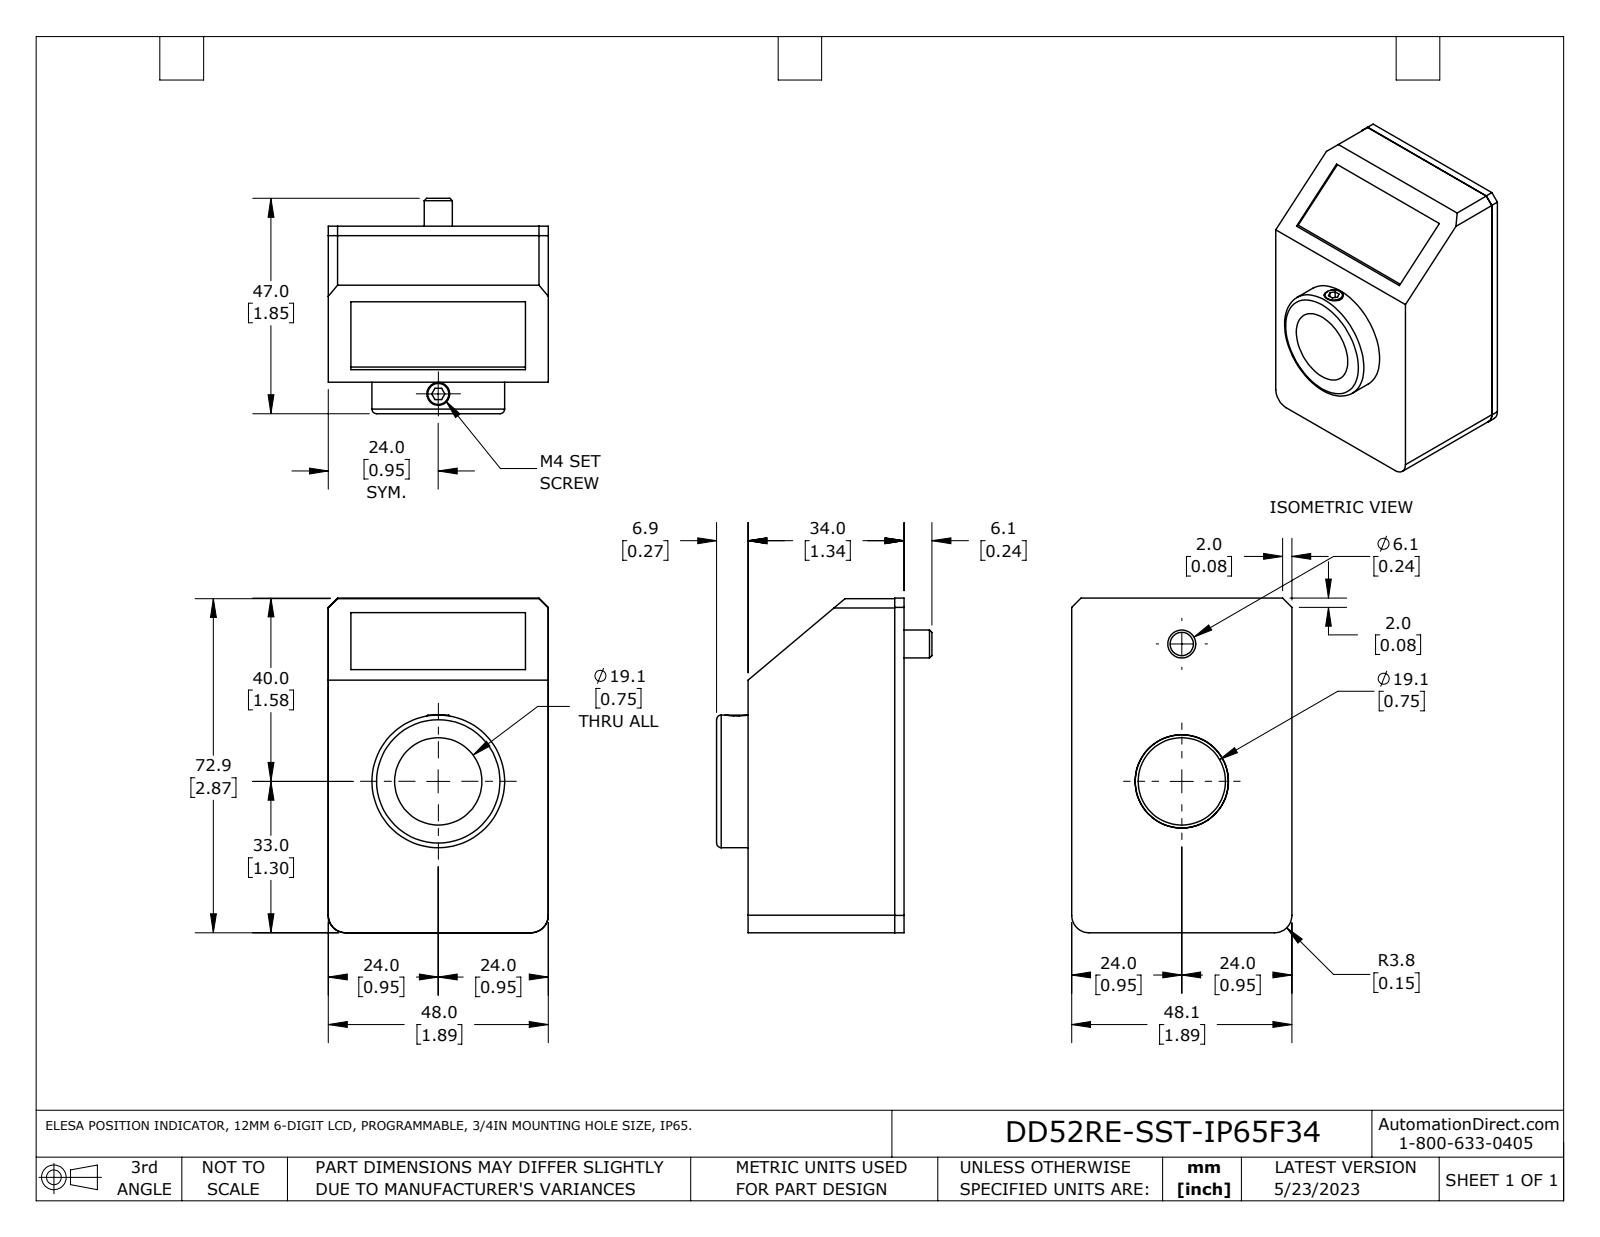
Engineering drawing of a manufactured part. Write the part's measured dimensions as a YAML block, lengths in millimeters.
part_name: "DD52RE-SST-IP65F34"
step_written_by: "SolidWorks 2021 (AUTOMOTIVE_DESIGN)"
units: millimeters
bodies: {solids: 1, faces: 51, planar: 35, cylindrical: 13, other: 3}
overall_size: [73.1, 48.1, 47]
volume: 101200
surface_area: 17680
round_holes:
  - {diameter: 5, count: 1}
  - {diameter: 19.1, count: 1}
  - {diameter: 20.4, count: 1}
  - {diameter: 29, count: 1}
round_bosses_or_shafts:
  - {diameter: 20.3, count: 1}
  - {diameter: 6.1, count: 1}
partial_cylinders:
  - {radius: 3.8, count: 4}
face_to_face_distances: [48, 34, 0.4, 72.9, 5.1, 29, 4.6, 0.5, 29.5, 48]
